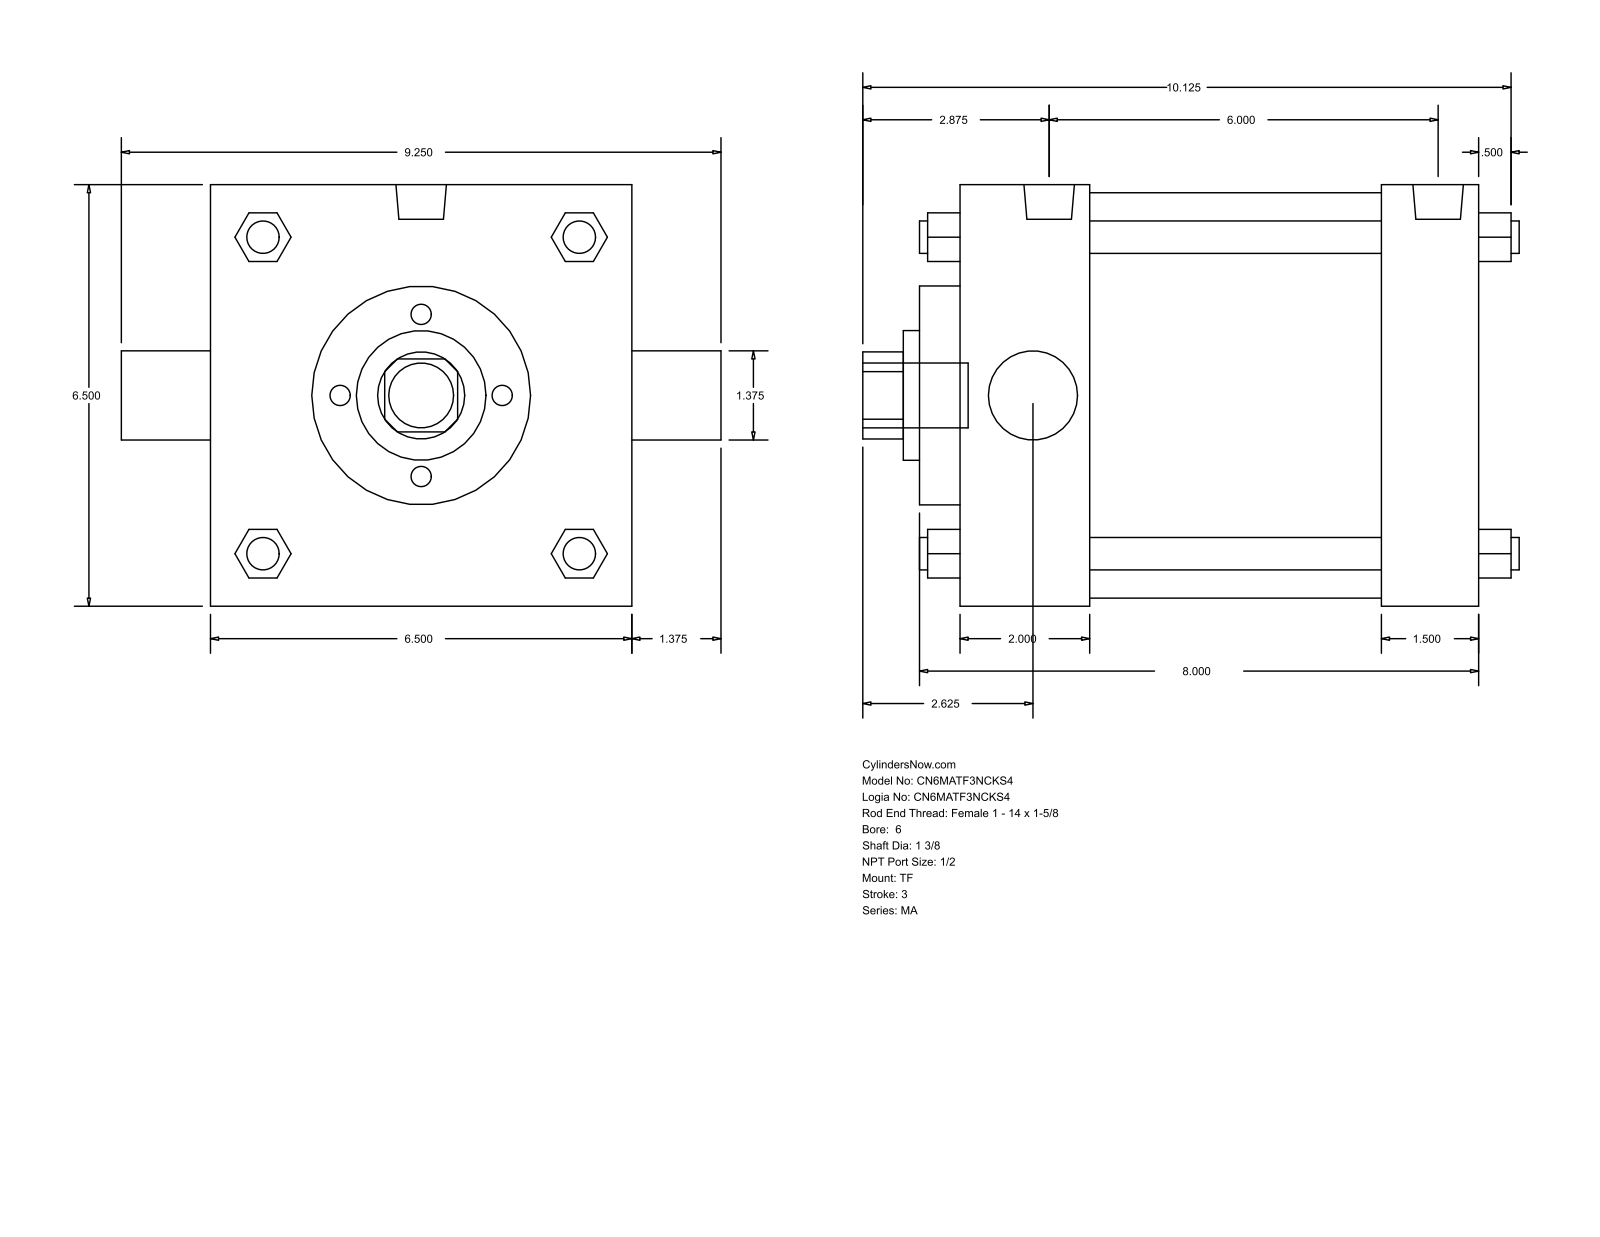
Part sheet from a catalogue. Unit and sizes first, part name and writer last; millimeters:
Units: millimetres
Overall size (bounding box): 257.18 × 234.95 × 165.1
Round holes (diameter × count): ⌀34.92 ×2, ⌀50.8 ×1, ⌀85.72 ×1, ⌀158.75 ×1
Round bosses / shafts (diameter × count): ⌀12.7 ×4, ⌀17.46 ×3, ⌀19.77 ×2, ⌀25.4 ×1
Partial cylindrical surfaces — rounded edges, fillets, slot ends (radius × count): R17.06 ×1
Main face-to-face distances: 165.1, 206.37, 50.8, 168.28, 155.57, 117.48, 38.09, 15.87, 66.67, 184.15
Bodies: 0 solids, 122 faces (93 planar, 29 cylindrical, 0 other)
Part name (STEP PRODUCT): MA_TF__0600_1.375
STEP written by: GSSL Pune (CONFIG_CONTROL_DESIGN)
